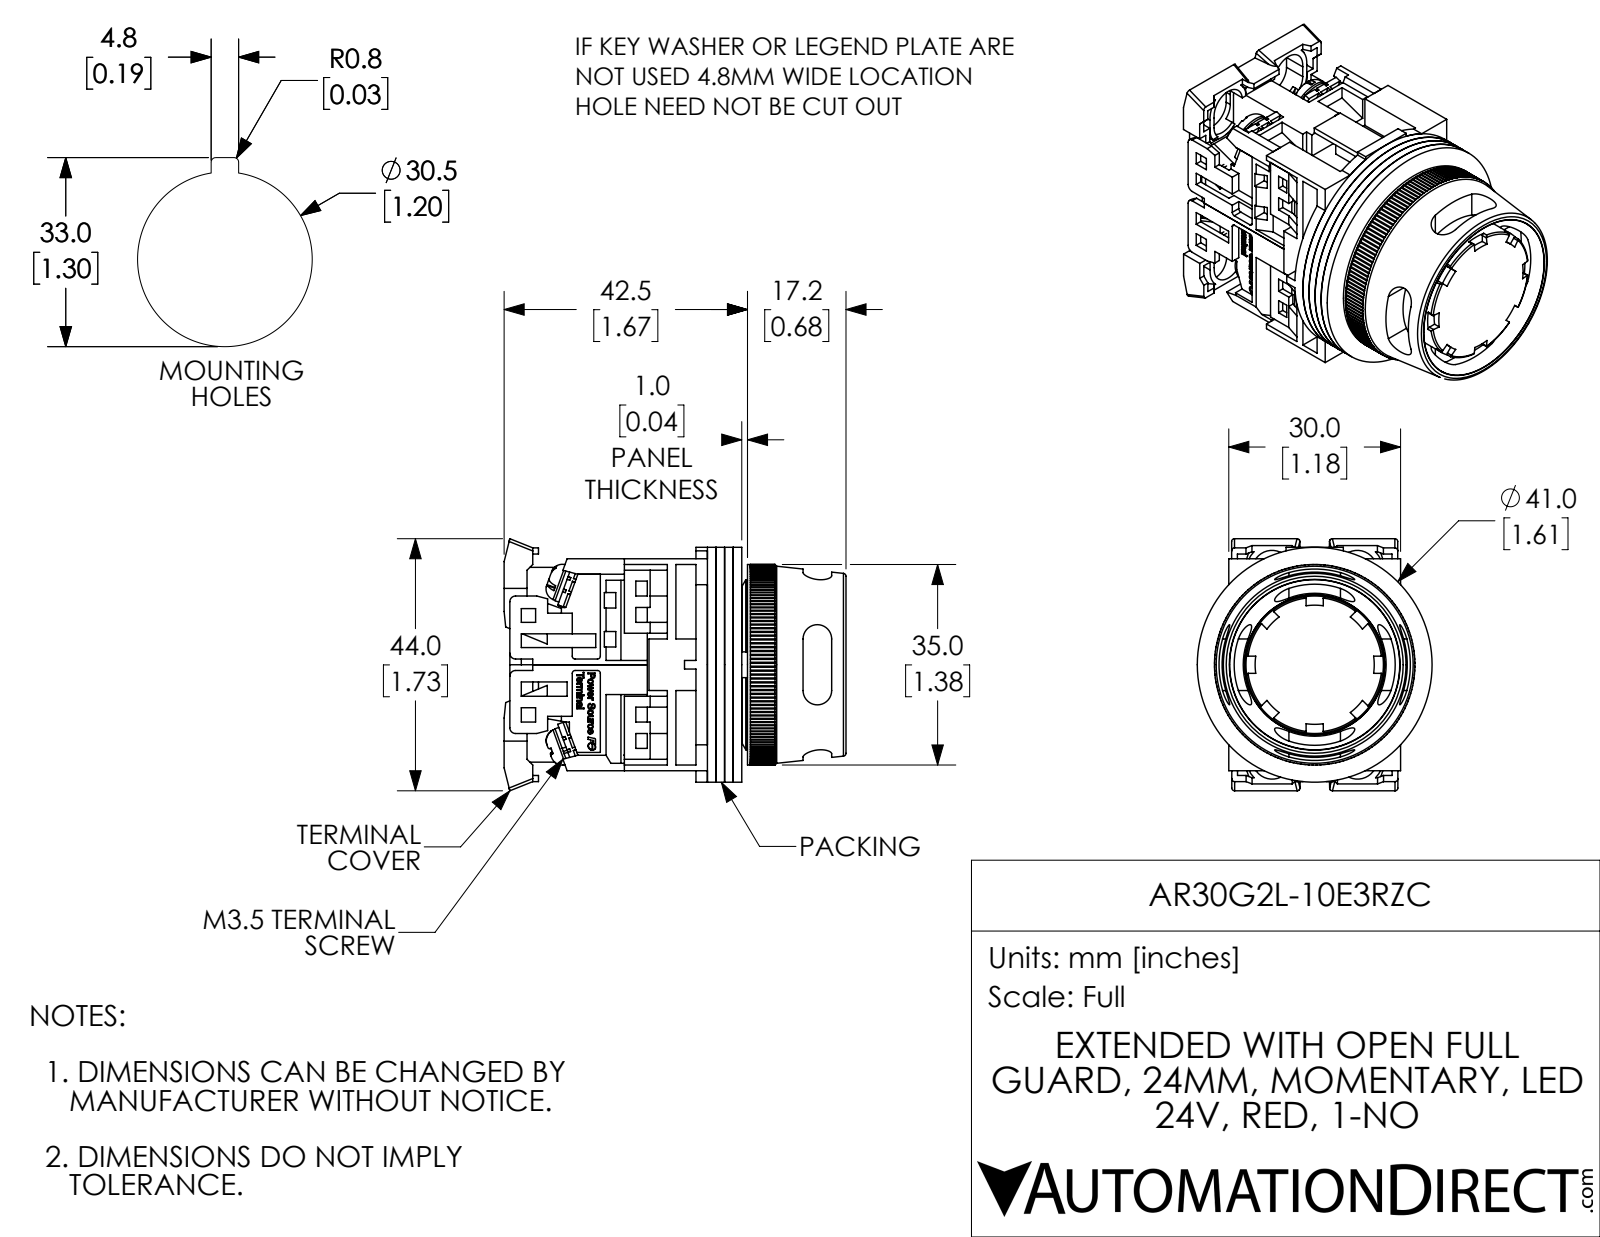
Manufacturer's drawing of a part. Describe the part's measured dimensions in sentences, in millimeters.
The part is named "AR30G2L-10E3RZC". Its 3-D file was written by "SolidWorks 2017 (AUTOMOTIVE_DESIGN)". It is 25 solids with 2179 faces: 1508 planar, 458 cylindrical and 213 other. Overall it measures 59.7 by 44 by 41 millimeters. Its volume is 35 100 cubic millimeters and its surface area 40 400 square millimeters. Round holes: 8 of diameter 3.5, 4 of diameter 3.6, 1 of diameter 3, 1 of diameter 12, 1 of diameter 18, 1 of diameter 18.5, 1 of diameter 20, 1 of diameter 24, 1 of diameter 31.8. Round bosses or shafts: 4 of diameter 6.6, 4 of diameter 3.5, 1 of diameter 41, 1 of diameter 35, 1 of diameter 30, 1 of diameter 22, 1 of diameter 19.7, 1 of diameter 14. Partial cylindrical surfaces (rounded edges, fillets, slot ends): 160 of radius 0.3, 16 of radius 0.3, 16 of radius 1.5, 12 of radius 0.5, 4 of radius 1, 4 of radius 2.5, 4 of radius 3.5, 4 of radius 4.5. The main face-to-face distances are 1.5, 3, 1, 4.5, 7, 36, 18.5, 20.6, 2, 34.5. The hole center spacings are 14.7, 15.5.
